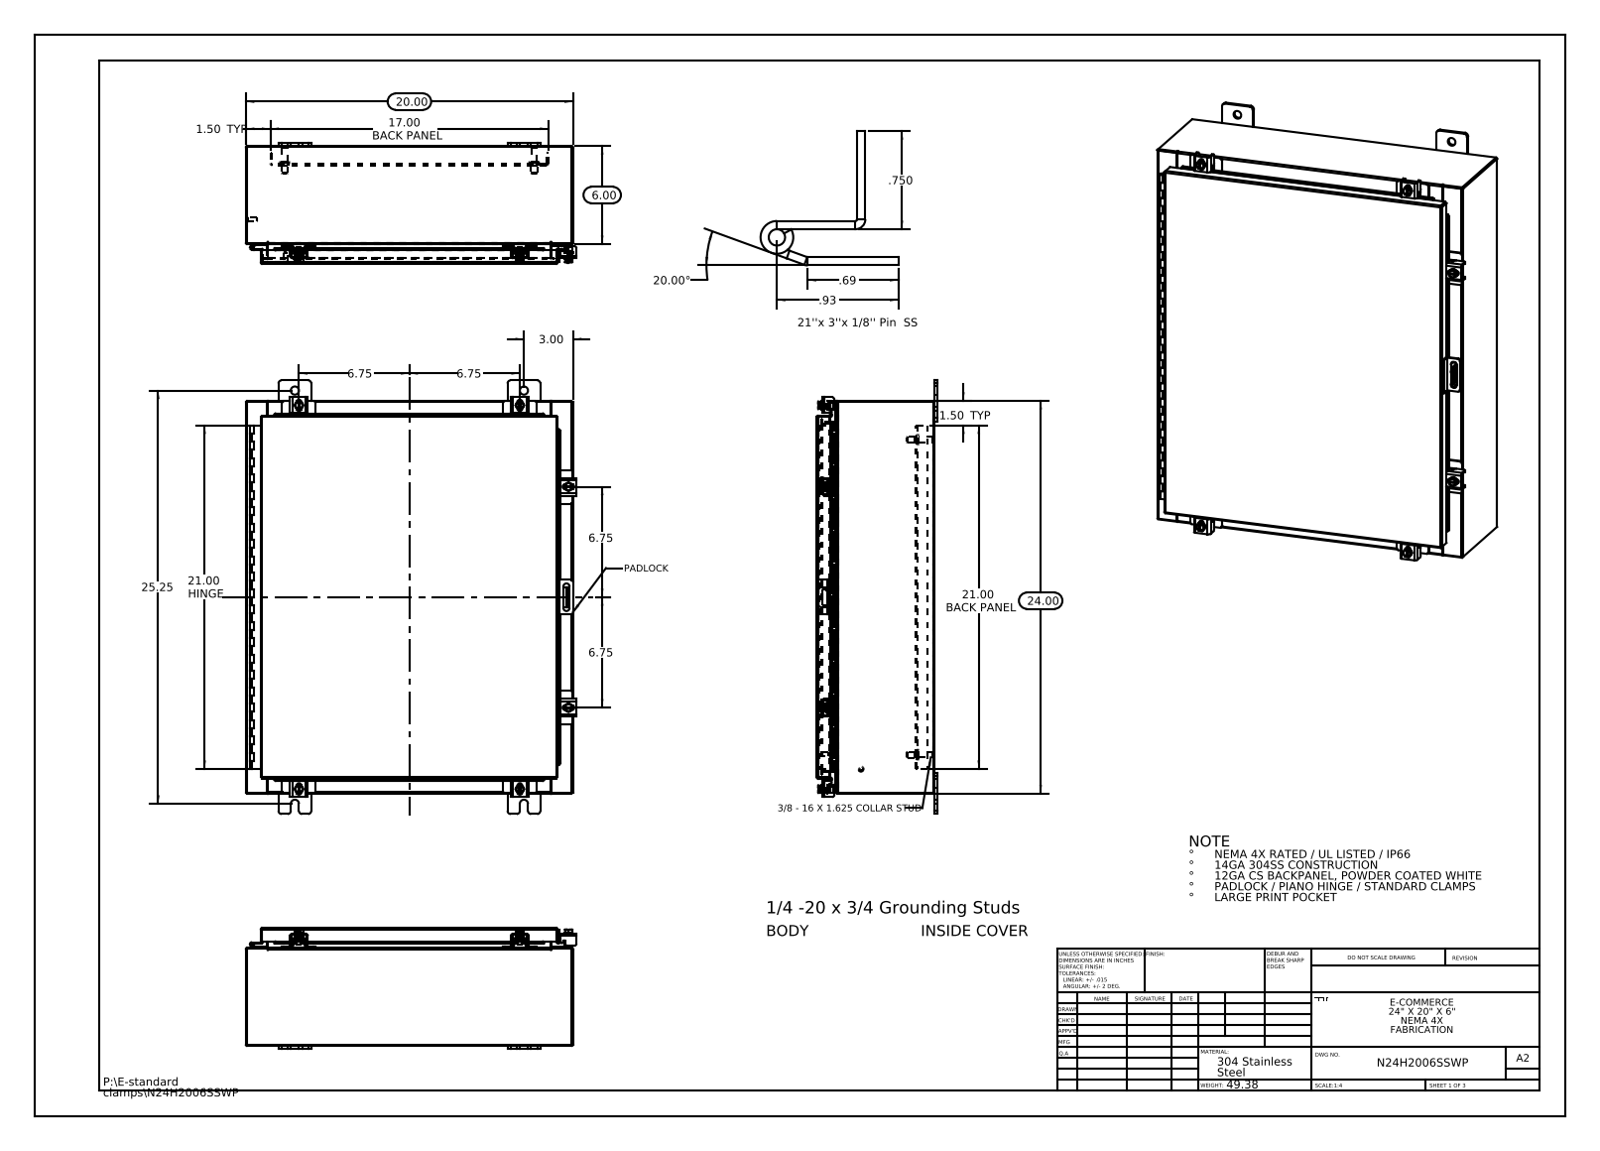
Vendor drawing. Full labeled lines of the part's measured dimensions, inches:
Part name (STEP PRODUCT): N24H2006SSWP Bottom; N24H2006SSWP 22101002; N24H2006SSWP Hinge Cover Side; N24H2006SSWP Mounting Studs (+8 more)
STEP written by: SolidWorks 2013 (CONFIG_CONTROL_DESIGN)
Units: inches
Bodies: 49 solids, 1735 faces (914 planar, 713 cylindrical, 108 other)
Overall size (bounding box): 26.5 × 20.211 × 7.389
Volume: 174 in³ · Surface area: 4 362 in²
Round holes (diameter × count): ⌀0.5 ×8, ⌀0.213 ×6, ⌀0.26 ×6, ⌀0.125 ×2
Round bosses / shafts (diameter × count): ⌀0.25 ×7, ⌀0.5 ×6, ⌀0.399 ×6, ⌀0.625 ×4, ⌀0.375 ×4, ⌀0.33 ×4, ⌀0.315 ×2, ⌀0.236 ×2
Partial cylindrical surfaces — rounded edges, fillets, slot ends (radius × count): R0.06 ×30, R0.013 ×25, R0.19 ×24, R0.088 ×21, R0.12 ×12, R0.141 ×12, R0.125 ×10, R0.05 ×9
Main face-to-face distances: 0.075, 7.126, 7.051, 7.201, 0.104, 1, 1.075, 6.051, 6.126, 1.179
Hole centre spacings: 21.369, 25.739, 13.5, 0.431, 0.934, 1.858, 2.275, 2.276
